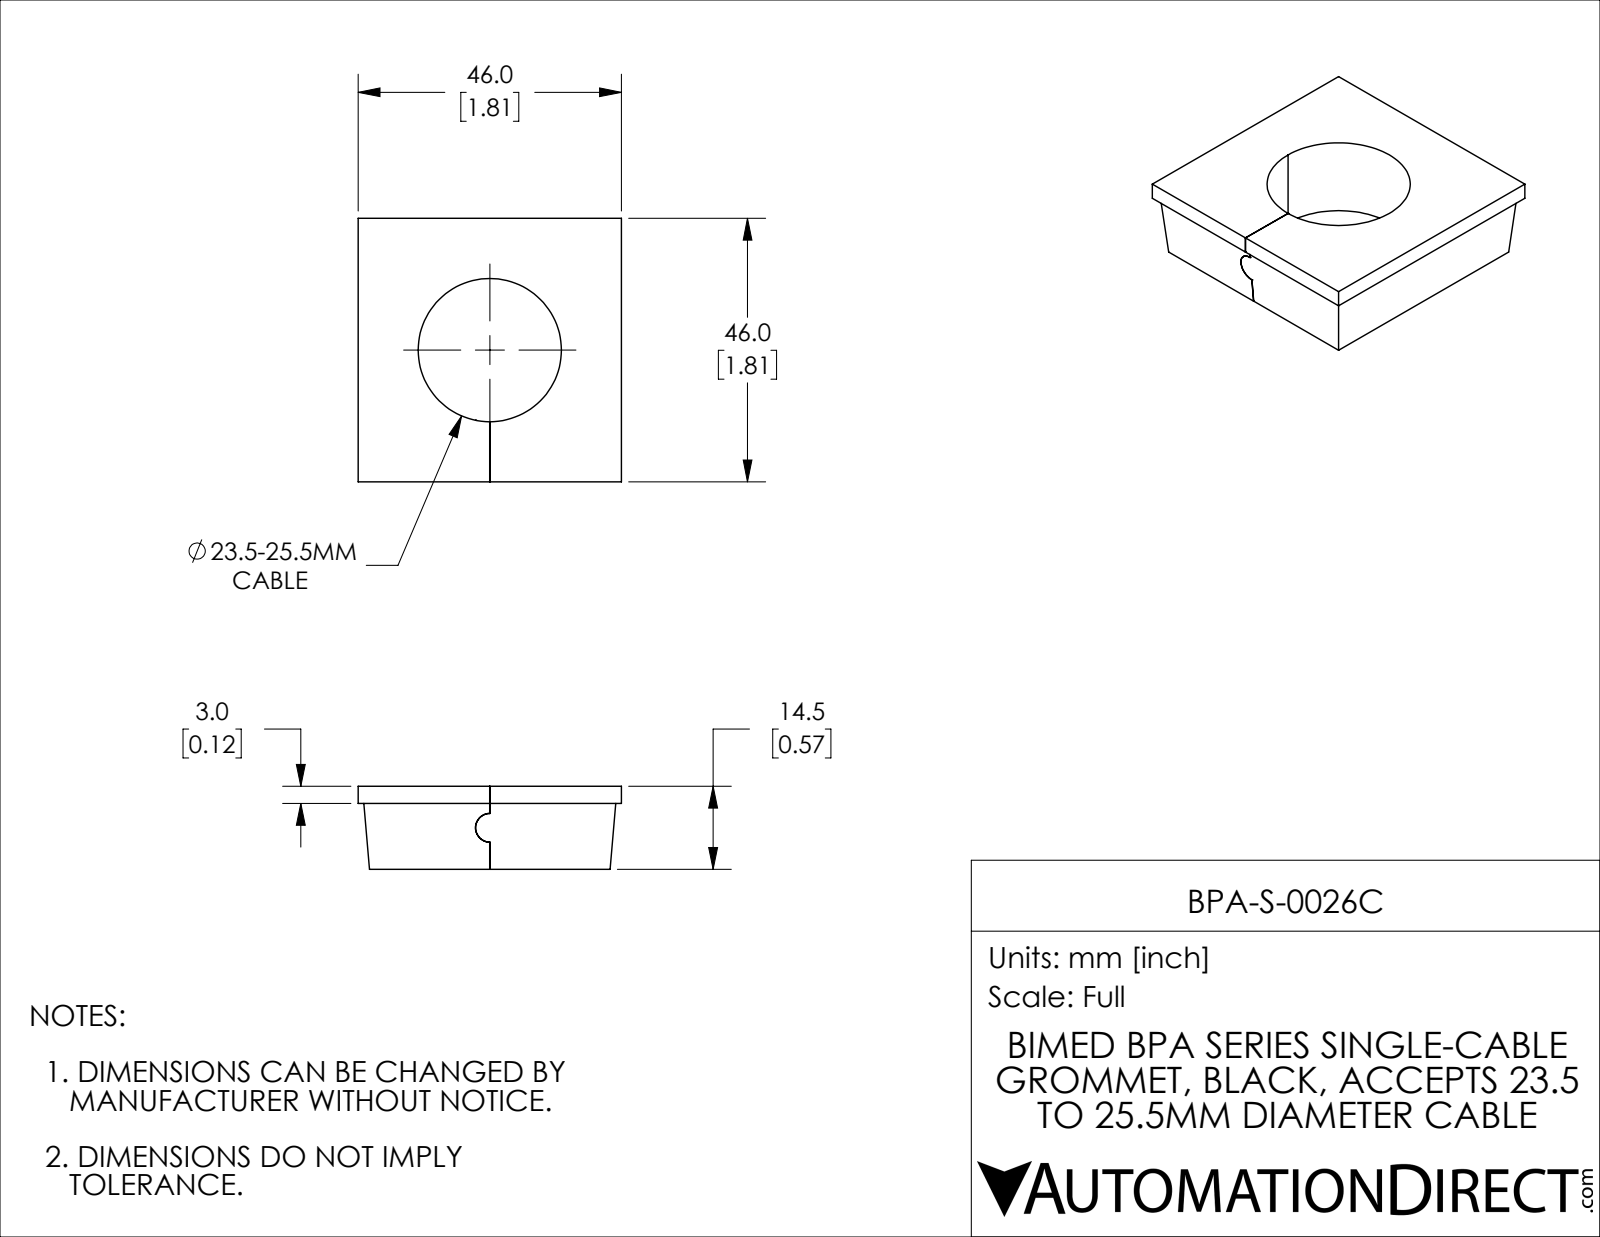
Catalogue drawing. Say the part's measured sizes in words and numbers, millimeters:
The part is named "BPA-S-0026C". Its 3-D file was written by "SolidWorks 2021 (CONFIG_CONTROL_DESIGN)". It is 1 solid with 22 faces: 17 planar, 5 cylindrical and 0 other. Overall it measures 46 by 46 by 14.5 millimeters. Its volume is 20 490 cubic millimeters and its surface area 7 077 square millimeters. Round holes: 1 of diameter 25. Partial cylindrical surfaces (rounded edges, fillets, slot ends): 1 of radius 2.5, 1 of radius 2.51. The main face-to-face distances are 14.5, 46, 11.5, 3, 22.99, 23.01.
